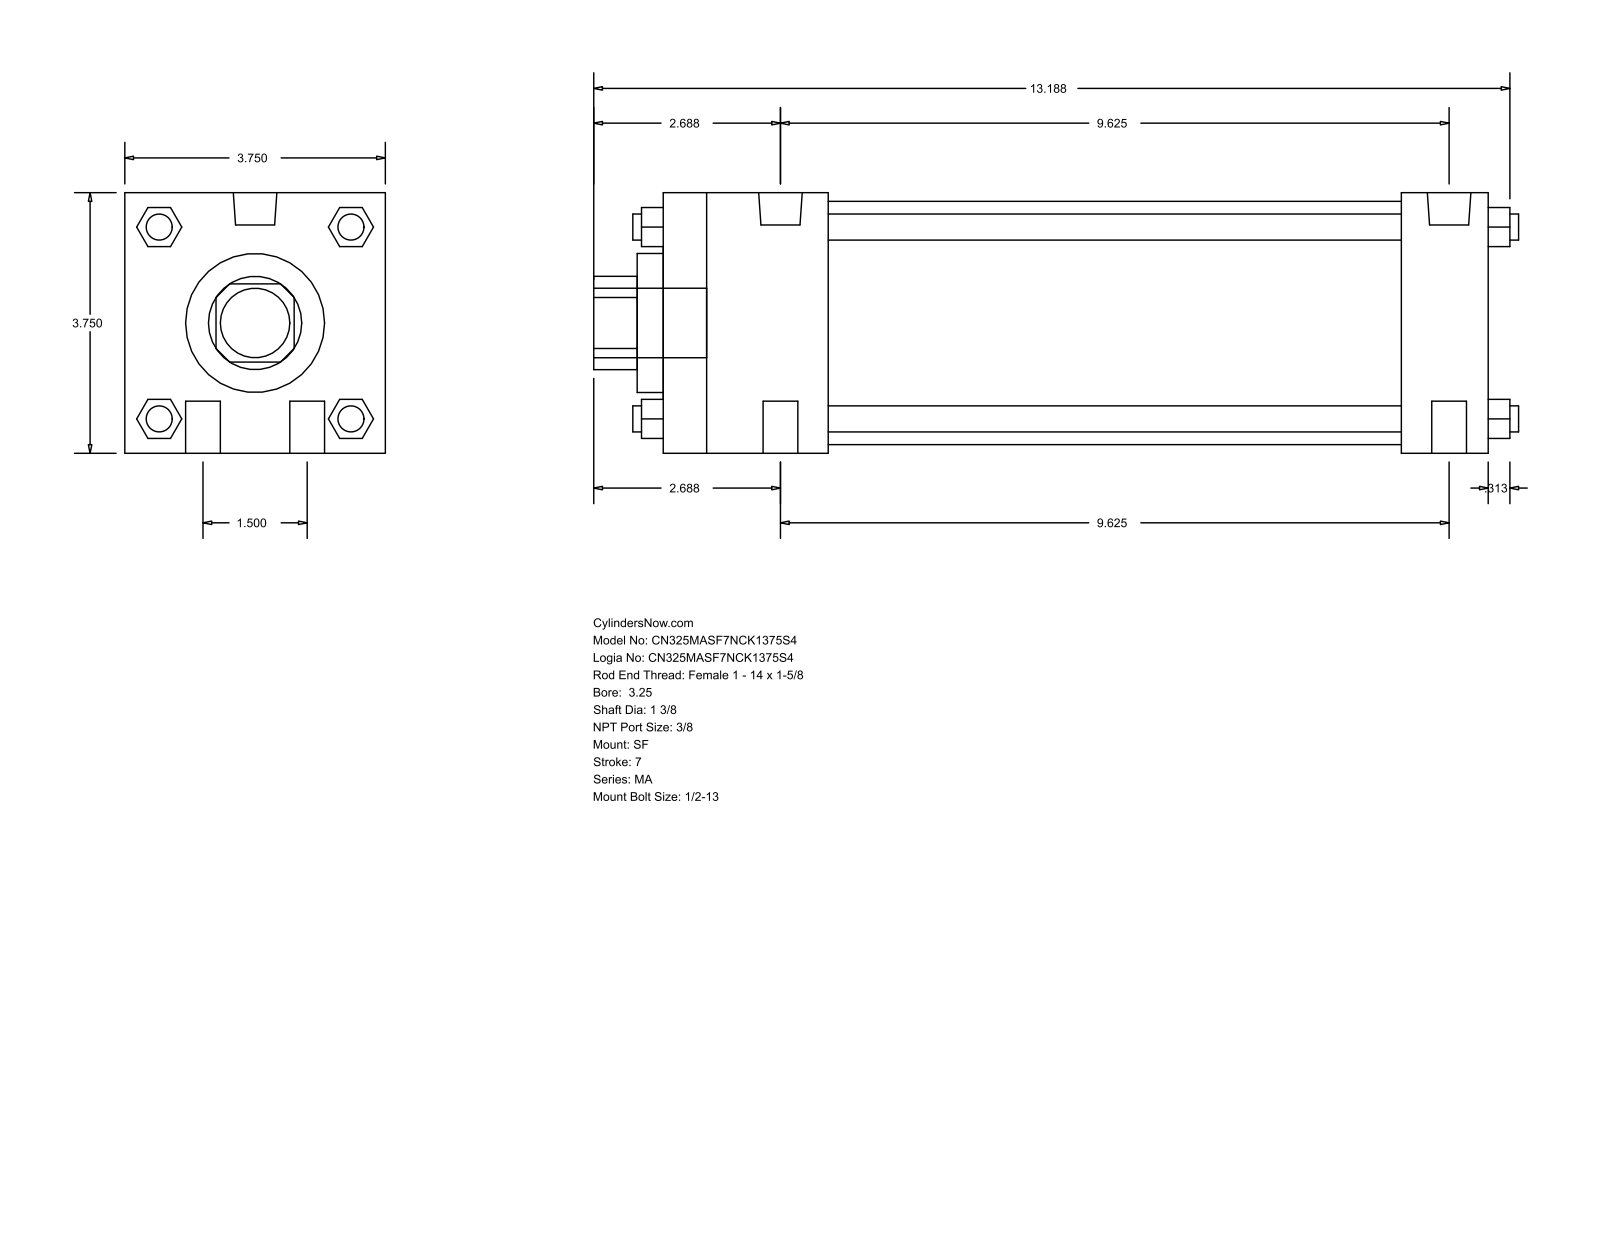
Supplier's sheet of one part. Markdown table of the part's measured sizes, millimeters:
| quantity | value |
| --- | --- |
| part name | MA_SF__0325_1.375 |
| STEP written by | GSSL Pune (CONFIG_CONTROL_DESIGN) |
| units | millimeters |
| bodies | 0 solids, 124 faces (94 planar, 30 cylindrical, 0 other) |
| overall size | 338.14 × 95.25 × 95.25 |
| round holes (diameter × count) | 34.92 × 1, 50.8 × 1, 88.9 × 1 |
| round bosses / shafts (diameter × count) | 12.7 × 4, 9.53 × 4, 15.93 × 2, 11.11 × 2, 25.4 × 1 |
| partial cylindrical surfaces (radius × count) | 17.06 × 1 |
| main face-to-face distances | 95.24, 301.62, 269.87, 31.75, 60.32, 209.55, 241.3, 9.52, 69.84, 279.39 |
